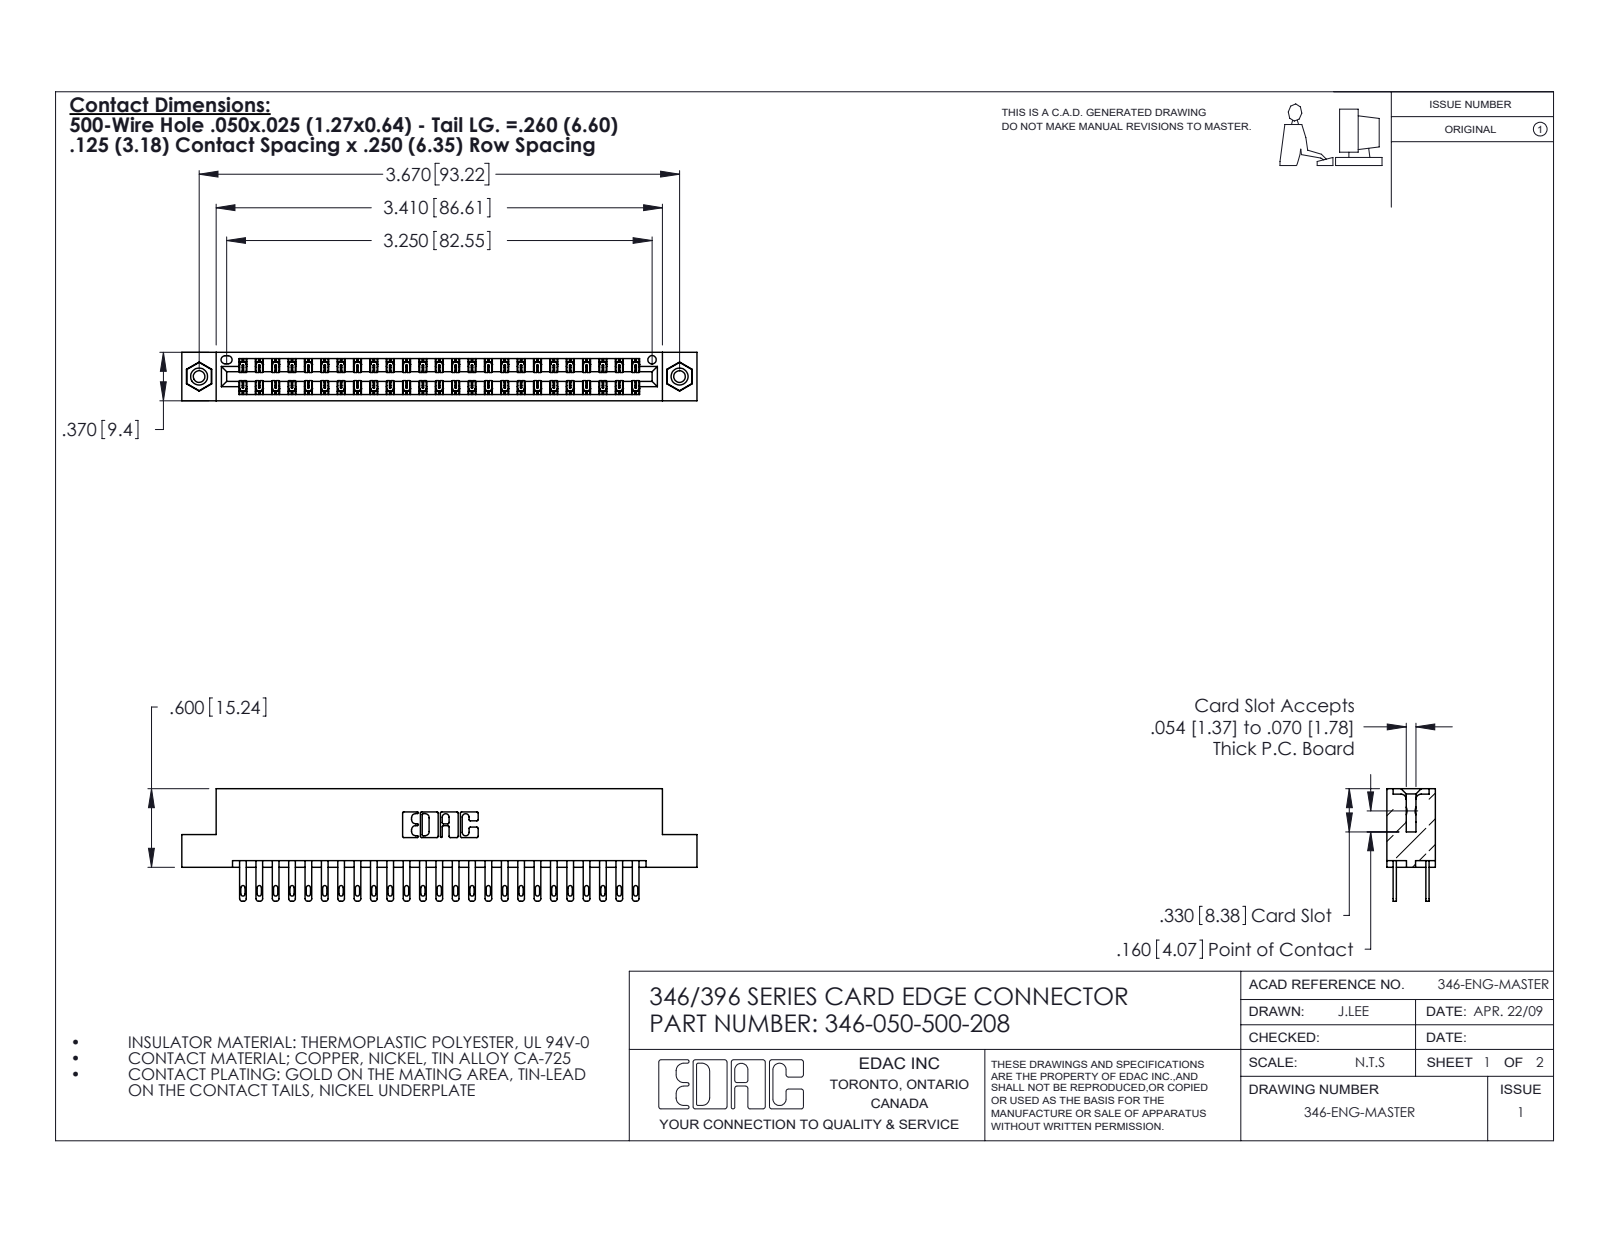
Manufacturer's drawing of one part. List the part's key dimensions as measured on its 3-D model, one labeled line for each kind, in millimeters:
Part name (STEP PRODUCT): 345-292-001_345-293-100; 346 Part_Flush Mounting Lugs - 0.156 Dia-TI; 346-050-500-208; 345-250-001_345-250-003-102
STEP written by: SolidWorks 2020 (CONFIG_CONTROL_DESIGN)
Units: millimetres
Bodies: 53 solids, 2582 faces (1558 planar, 1008 cylindrical, 16 other)
Overall size (bounding box): 99.9 × 21.8 × 9.4
Volume: 9 770 mm³ · Surface area: 13 690 mm²
Round holes (diameter × count): ⌀2.3 ×2, ⌀3.2 ×2, ⌀4 ×2, ⌀1.6 ×1
Round bosses / shafts (diameter × count): ⌀3.9 ×2
Partial cylindrical surfaces — rounded edges, fillets, slot ends (radius × count): R0.2 ×75, R0.4 ×50, R0.5 ×50, R0.3 ×22, R0.2 ×6, R0.8 ×6, R0.7 ×3, R0.4 ×2
Main face-to-face distances: 1.2, 8.2, 6.4, 9.4, 1.8, 7.6, 0.6, 7, 3.8, 5.6
Hole centre spacings: 6.2, 87.9, 93.2
